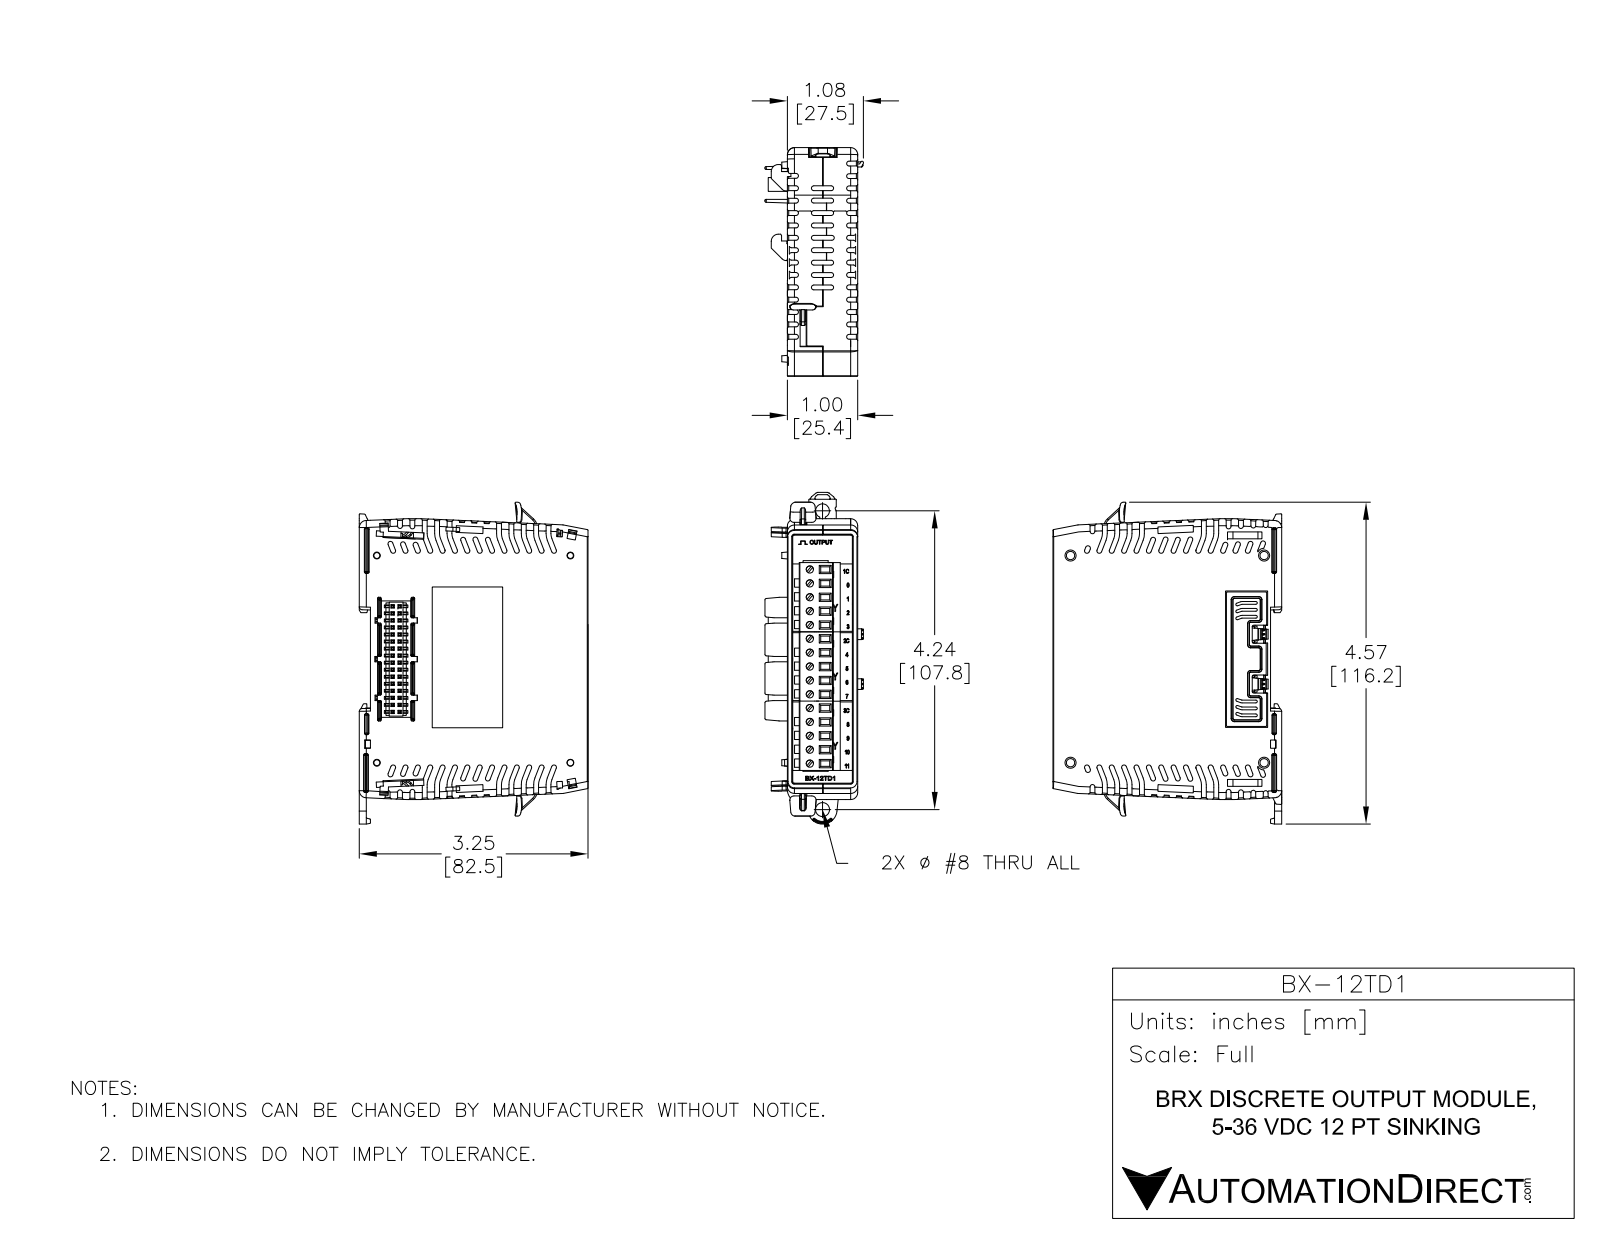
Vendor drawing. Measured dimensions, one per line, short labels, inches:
name: BX-12TD1
written by: SolidWorks 2017 (AUTOMOTIVE_DESIGN)
unit: in
bodies: 15 solids, 3752 faces (2650 planar, 573 cylindrical, 529 other)
size: 4.586 × 3.311 × 1.402
volume: 11.6 in³; area: 72.79 in²
holes: 2× ⌀0.047, 2× ⌀0.065, 2× ⌀0.118, 2× ⌀0.118, 1× ⌀0.199
bosses: 2× ⌀0.062, 2× ⌀0.059
rounds: 102× R0.005, 47× R0.01, 34× R0.02, 24× R0.005, 21× R0.008, 15× R0.122, 14× R0.117, 13× R0.039
face distances: 1, 3.211, 0.1, 3.22, 0.475, 0.157, 3.053, 3.063, 0.787, 0.63
hole spacings: 0.1, 0.824, 0.919, 1.3, 2.093, 2.193, 2.585, 2.617
